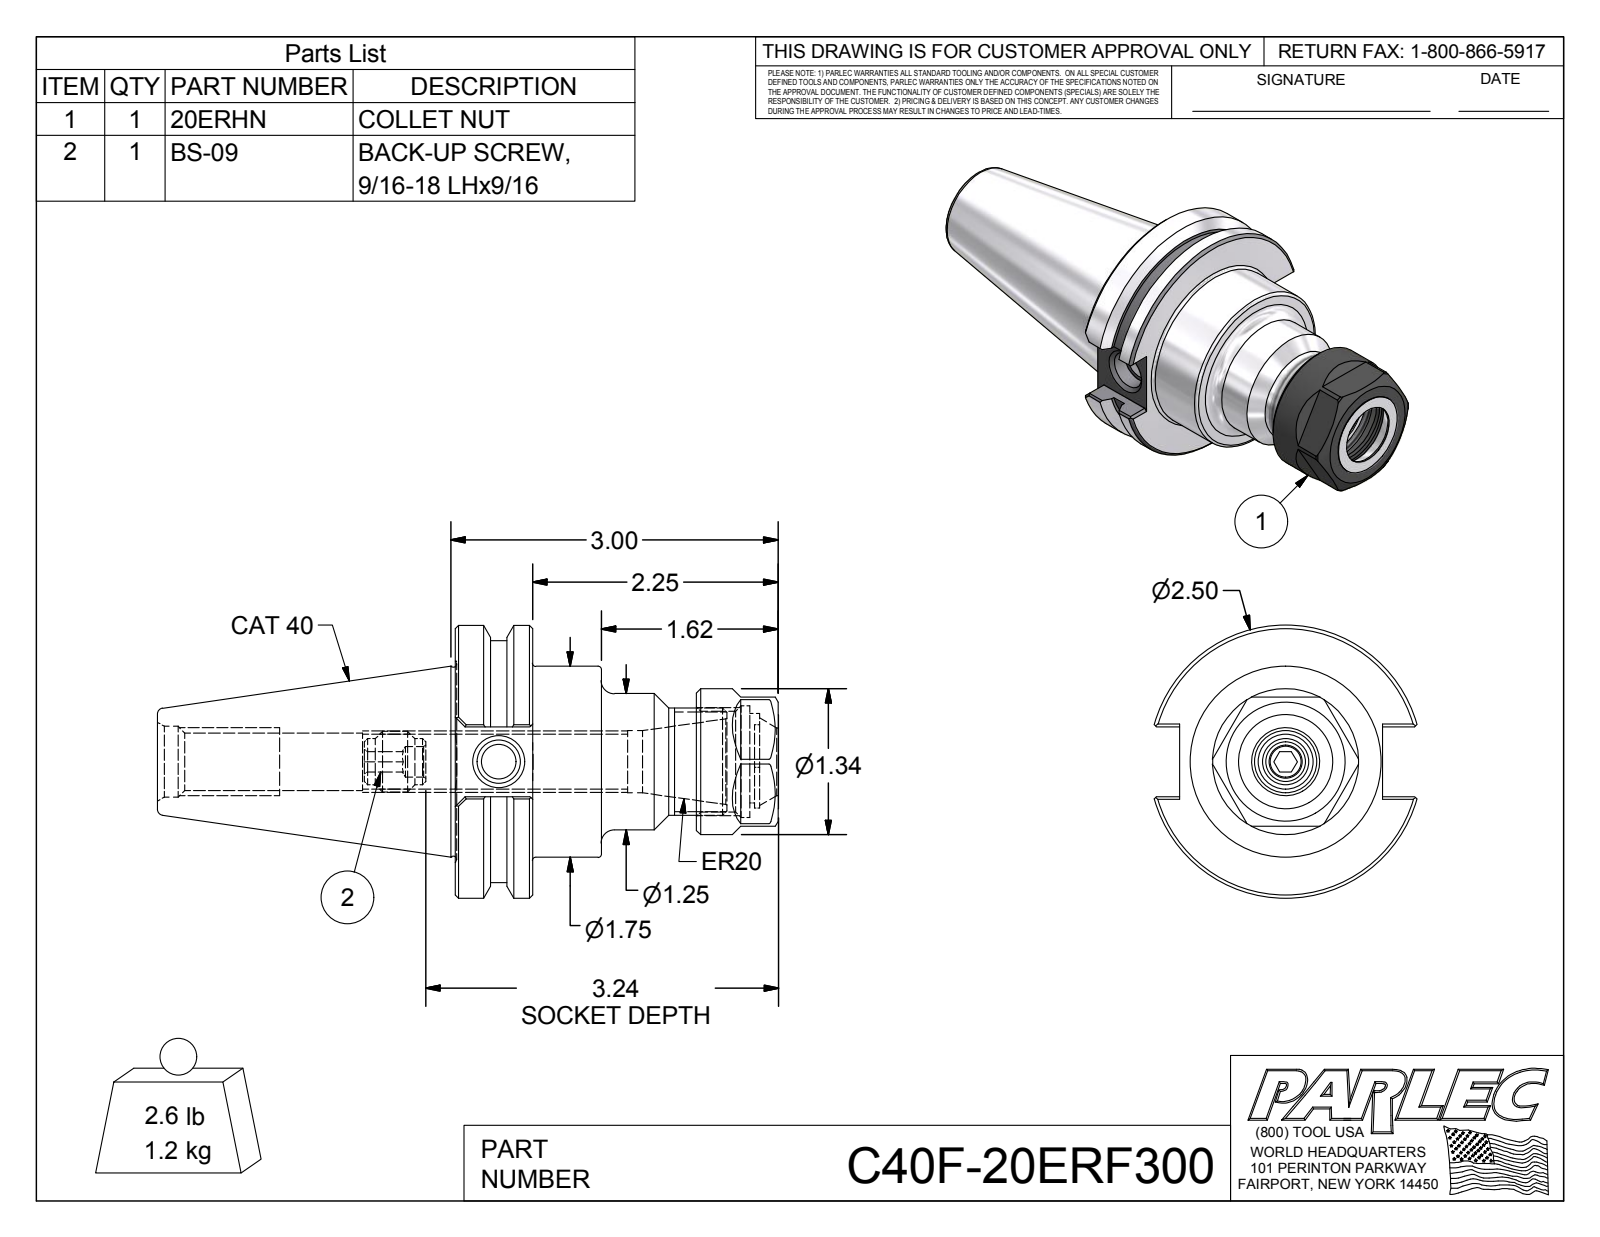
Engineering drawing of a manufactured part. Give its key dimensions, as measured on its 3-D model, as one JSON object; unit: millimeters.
{"part_name": "C40F-20ER3-1; 20ERHN; BS-09; C40F-20ERF300", "step_written_by": "Autodesk Inventor 2016 (AUTOMOTIVE_DESIGN)", "units": "millimeters", "bodies": {"solids": 3, "faces": 136, "planar": 65, "cylindrical": 26, "other": 45}, "overall_size": [144.46, 63.5, 61.11], "volume_mm3": 148884, "surface_area_mm2": 32339, "round_holes": [[7.14, 1], [8, 1], [10.13, 1], [12.75, 1], [13.39, 1], [14.48, 1], [15.49, 1], [16.46, 1], [23.5, 1], [26, 1]], "round_bosses_or_shafts": [[63.5, 1], [56.26, 1], [44.45, 1], [34, 1], [31.75, 1], [25, 1], [14.1, 1], [10.72, 1]], "partial_cylinders_radius": [[9.47, 1], [10.55, 1], [10.75, 1]], "face_to_face_distances": [18.04, 75.19, 57.15, 30, 34.04, 16, 41.15, 56.12, 38.08, 22.08]}
